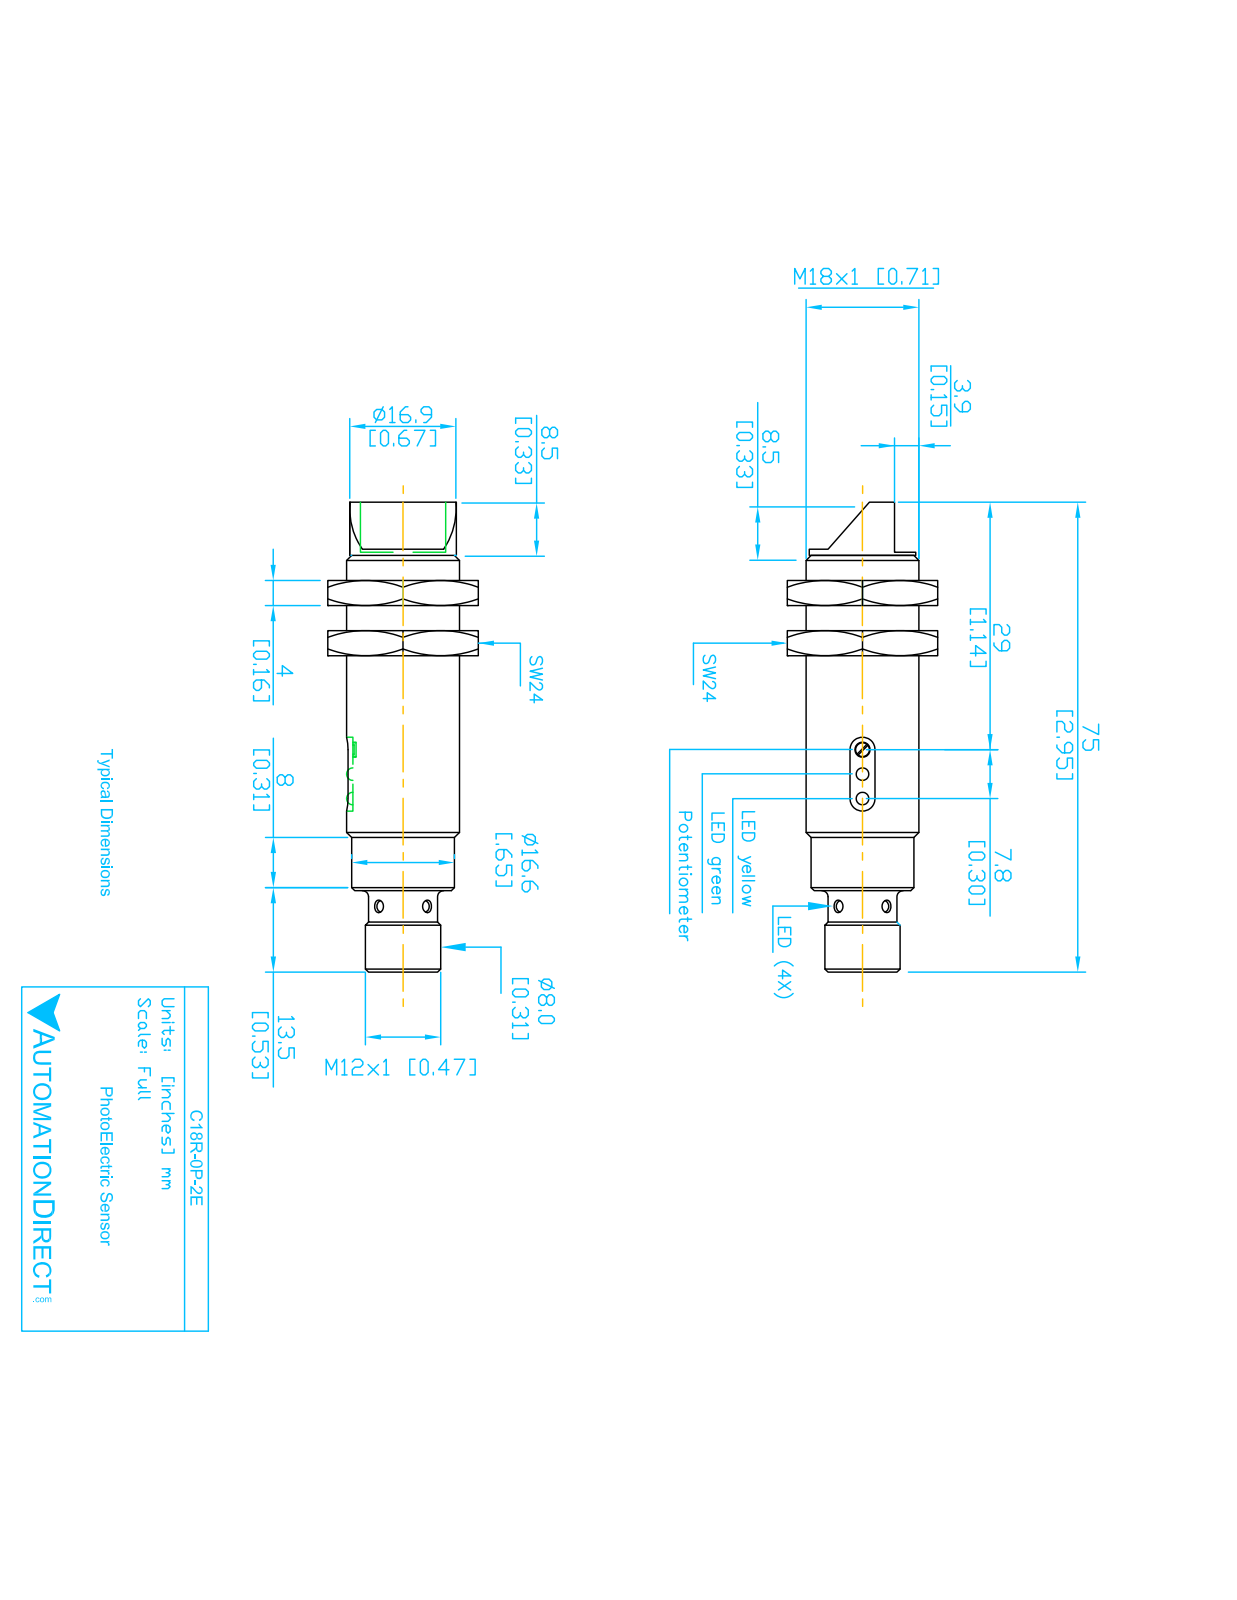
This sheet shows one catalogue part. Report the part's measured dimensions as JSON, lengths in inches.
{"part_name": "C18R-0P-2E", "step_written_by": "SolidWorks 2017 (AUTOMOTIVE_DESIGN)", "units": "inches", "bodies": {"solids": 2, "faces": 85, "planar": 18, "cylindrical": 35, "other": 32}, "overall_size": [2.957, 0.709, 0.709], "volume_in3": 0.905, "surface_area_in2": 7.969, "round_holes": [[0.118, 2], [0.335, 1]], "round_bosses_or_shafts": [[0.04, 4], [0.709, 1], [0.665, 1], [0.646, 1], [0.459, 1], [0.415, 1]], "partial_cylinders_radius": [[0.015, 6], [0.02, 2], [0.202, 1]], "face_to_face_distances": [0.169, 0.512, 0.343, 2.445, 2.614, 2.957, 0.28, 2.165, 2.335, 2.677]}
